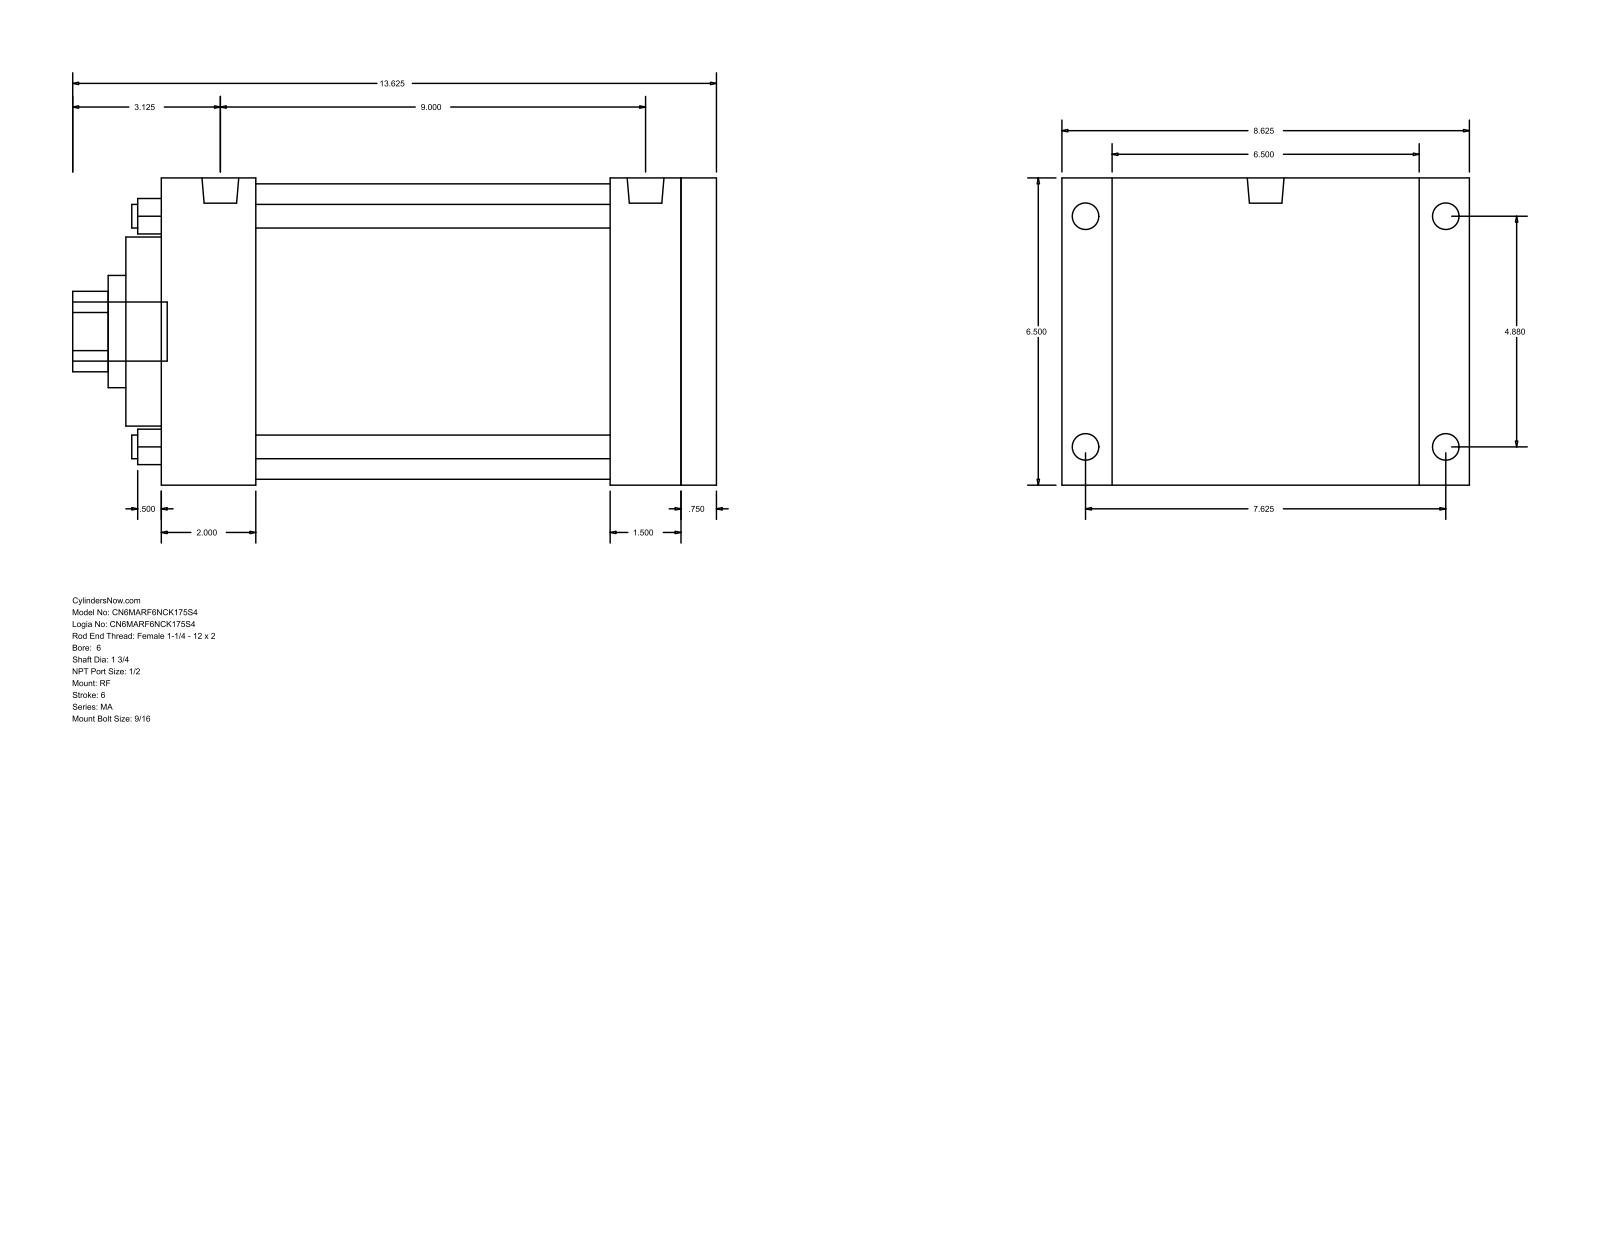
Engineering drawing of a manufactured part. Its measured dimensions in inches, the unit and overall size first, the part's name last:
Units: inches
Overall size (bounding box): 13.625 × 8.625 × 6.5
Round holes (diameter × count): ⌀0.5 ×4, ⌀1.75 ×1, ⌀2.375 ×1, ⌀4 ×1, ⌀6.25 ×1
Round bosses / shafts (diameter × count): ⌀0.687 ×4, ⌀0.563 ×4, ⌀0.778 ×2, ⌀1.25 ×1
Partial cylindrical surfaces — rounded edges, fillets, slot ends (radius × count): R0.852 ×1
Main face-to-face distances: 6.5, 11.75, 0.75, 11, 2, 9, 9.75, 9.5, 7.5, 1.5
Hole centre spacings: 3.451, 4.88, 6.902
Bodies: 0 solids, 94 faces (65 planar, 29 cylindrical, 0 other)
Part name (STEP PRODUCT): MA_RF__0600_1.75
STEP written by: GSSL Pune (CONFIG_CONTROL_DESIGN)
